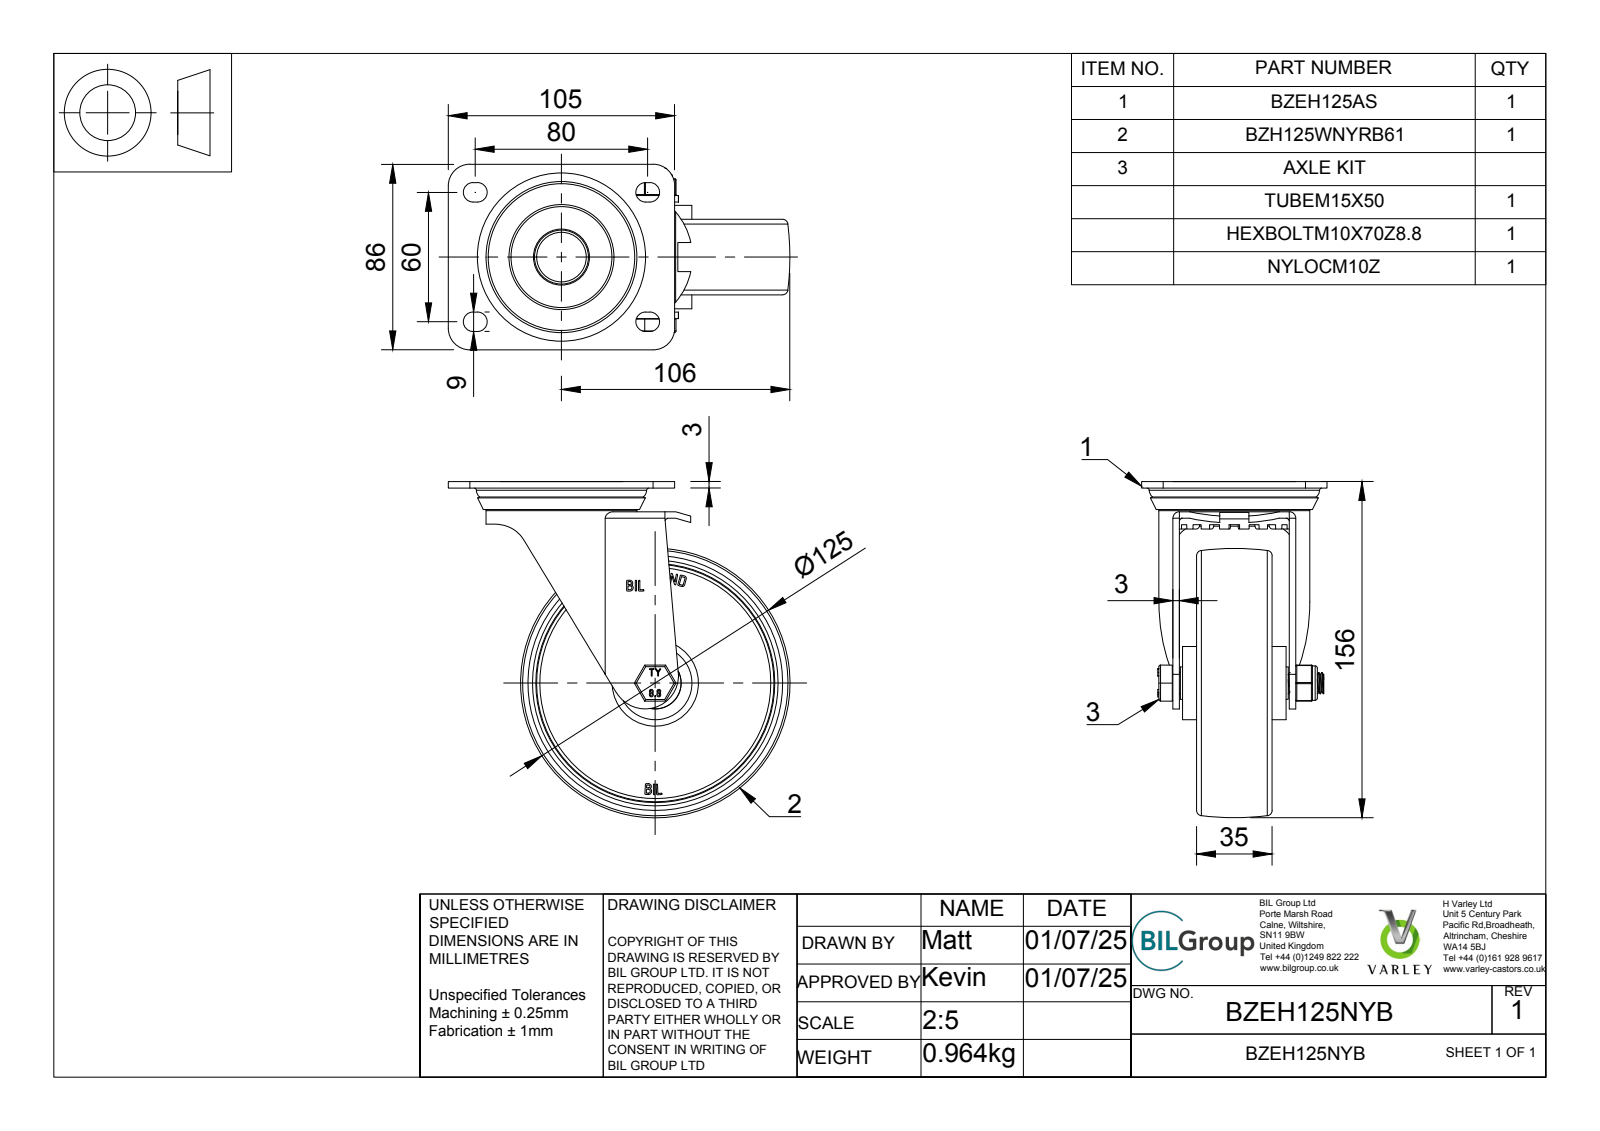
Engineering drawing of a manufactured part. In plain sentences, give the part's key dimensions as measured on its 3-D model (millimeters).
The part is named "BZEH125NYB v4; BZEH125AS - 2 v1; ZINC PLATED, PRESSED STEEL TOP PLATE; ZINC PLATED, PRESSED STEEL TOP PLATE Geometry (+7 more)". Its 3-D file was written by "Autodesk Translation Framework v14.10.0.0 (AUTOMOTIVE_DESIGN)". It is 39 solids with 731 faces: 395 planar, 147 cylindrical and 189 other. Overall it measures 158.5 by 156 by 86 millimeters. Its volume is 303 998 cubic millimeters and its surface area 133 465 square millimeters. Round holes: 1 of diameter 10, 1 of diameter 10.25, 1 of diameter 10.5, 1 of diameter 12, 1 of diameter 15, 1 of diameter 34, 1 of diameter 44.58, 1 of diameter 64. Round bosses or shafts: 8 of diameter 4, 2 of diameter 16, 1 of diameter 70, 1 of diameter 54, 1 of diameter 34, 1 of diameter 25, 1 of diameter 24, 1 of diameter 22.75. Partial cylindrical surfaces (rounded edges, fillets, slot ends): 18 of radius 0.5, 8 of radius 4.5, 6 of radius 0.75, 4 of radius 1.5, 4 of radius 10, 2 of radius 3, 2 of radius 31.61, 1 of radius 9.38. The main face-to-face distances are 3, 9, 24, 33, 54, 21, 30, 8, 6.5, 14.
